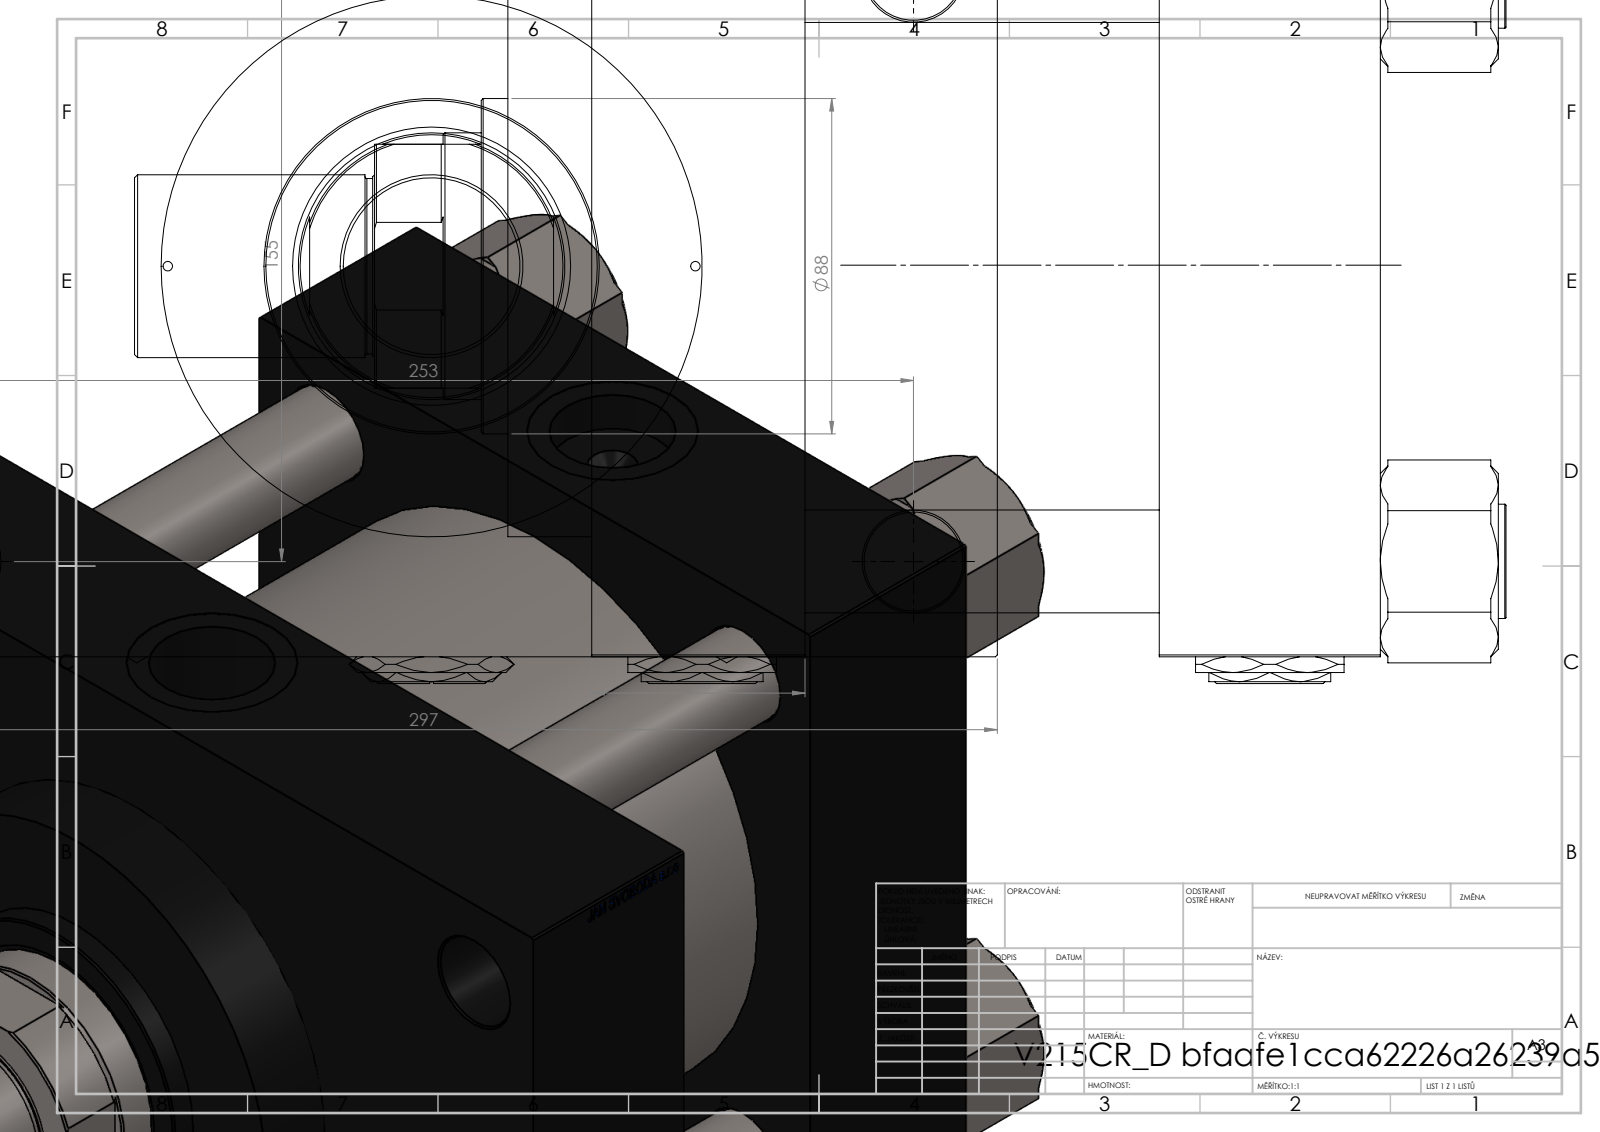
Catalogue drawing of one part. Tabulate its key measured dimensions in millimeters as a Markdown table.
| quantity | value |
| --- | --- |
| part name | Zatka_pro_OIL_PORT; V215_VC_A; V215CR_D_Body; V215CR_VCP_D (+3 more) |
| STEP written by | SolidWorks 2019 (CONFIG_CONTROL_DESIGN) |
| units | millimeters |
| bodies | 14 solids, 1270 faces (598 planar, 106 cylindrical, 566 other) |
| overall size | 360 × 297 × 213.57 |
| volume | 7 984 000 mm³ |
| surface area | 751 674 mm² |
| round holes (diameter × count) | 26 × 4, 27 × 4, 2.5 × 2, 7 × 2, 33.24 × 2, 45 × 2, 46.5 × 1, 70 × 1, 73 × 1, 120 × 1, 142 × 1, 160 × 1 |
| round bosses / shafts (diameter × count) | 30 × 4, 166 × 1, 88 × 1, 48 × 1, 46 × 1 |
| partial cylindrical surfaces (radius × count) | 34 × 1 |
| main face-to-face distances | 58, 151, 93, 149, 207, 56, 205, 46, 251, 72 |
| hole center spacings | 49.05, 77.88, 96.35, 109.53, 148.35, 154.9, 162.53, 165.89 |
